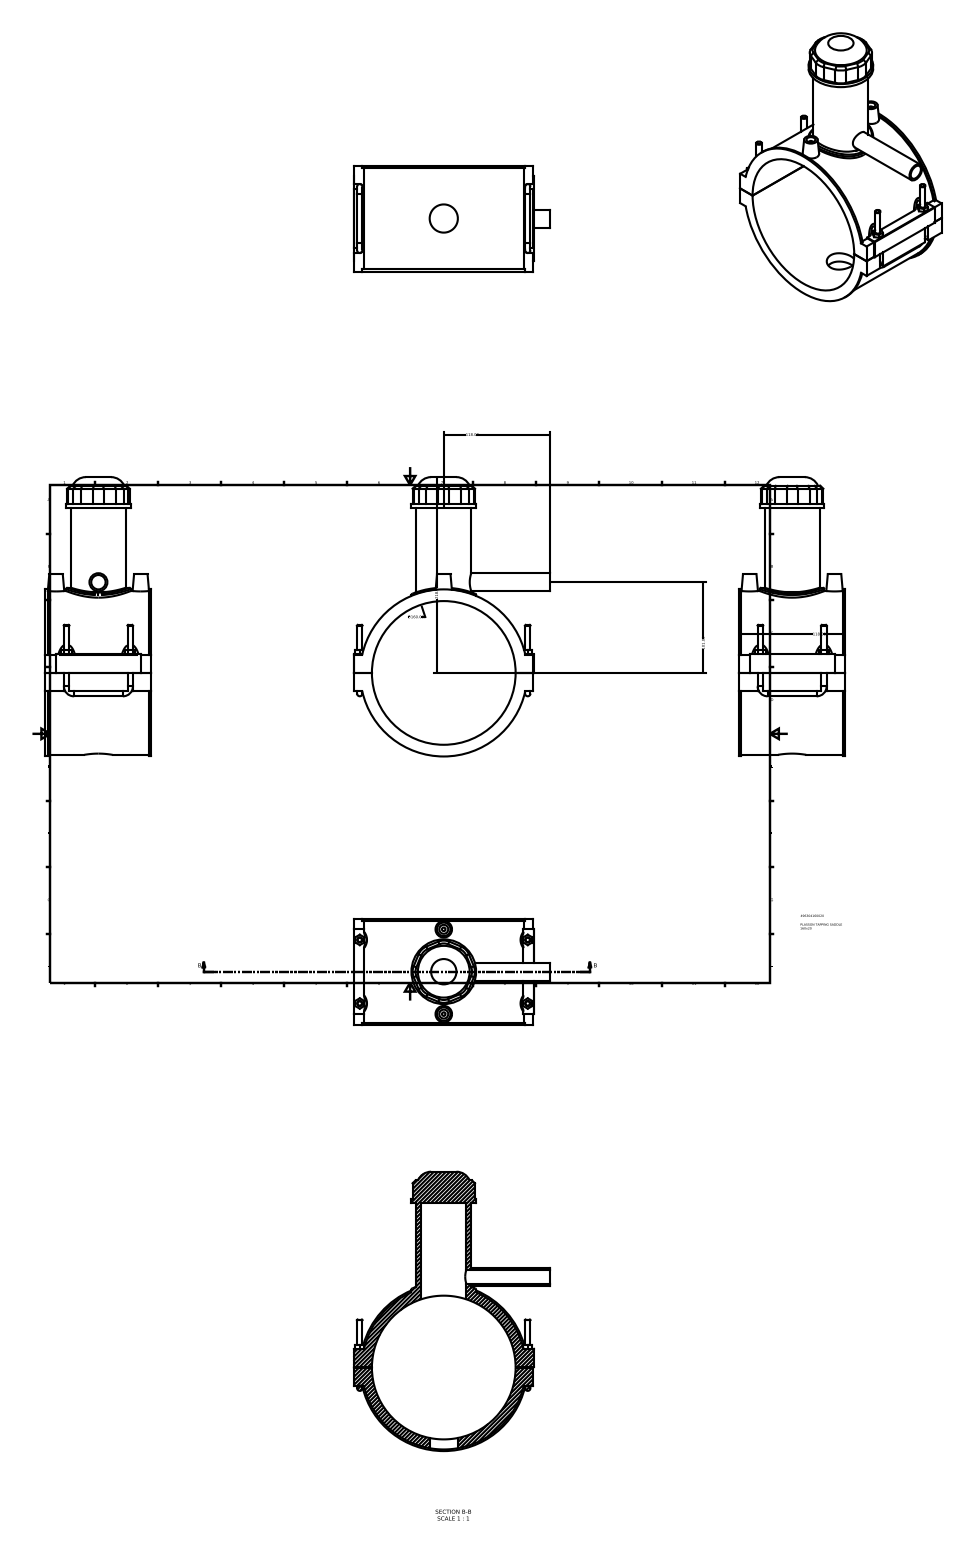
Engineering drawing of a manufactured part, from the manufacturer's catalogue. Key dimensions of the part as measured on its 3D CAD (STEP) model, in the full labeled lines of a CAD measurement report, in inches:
Part name (STEP PRODUCT): 496304160020
STEP written by: Autodesk Inventor 2015 (AUTOMOTIVE_DESIGN)
Units: inches
Bodies: 1 solid, 185 faces (112 planar, 47 cylindrical, 26 other)
Overall size (bounding box): 12.245 × 8.602 × 4.646
Volume: 61 in³ · Surface area: 342.7 in²
Round holes (diameter × count): ⌀0.394 ×2, ⌀0.63 ×1, ⌀1.235 ×1, ⌀1.984 ×1, ⌀6.299 ×1
Round bosses / shafts (diameter × count): ⌀0.236 ×6, ⌀0.157 ×2, ⌀7.325 ×1, ⌀7.181 ×1, ⌀2.835 ×1, ⌀2.409 ×1, ⌀0.787 ×1
Partial cylindrical surfaces — rounded edges, fillets, slot ends (radius × count): R0.63 ×8, R0.118 ×4, R0.295 ×4, R0.02 ×1, R3.734 ×1
Main face-to-face distances: 4.646, 0.039, 7.874, 7.226, 7.222, 7.835, 0.785, 0.789, 8.012, 7.913
Hole centre spacings: 1.858, 3.717
